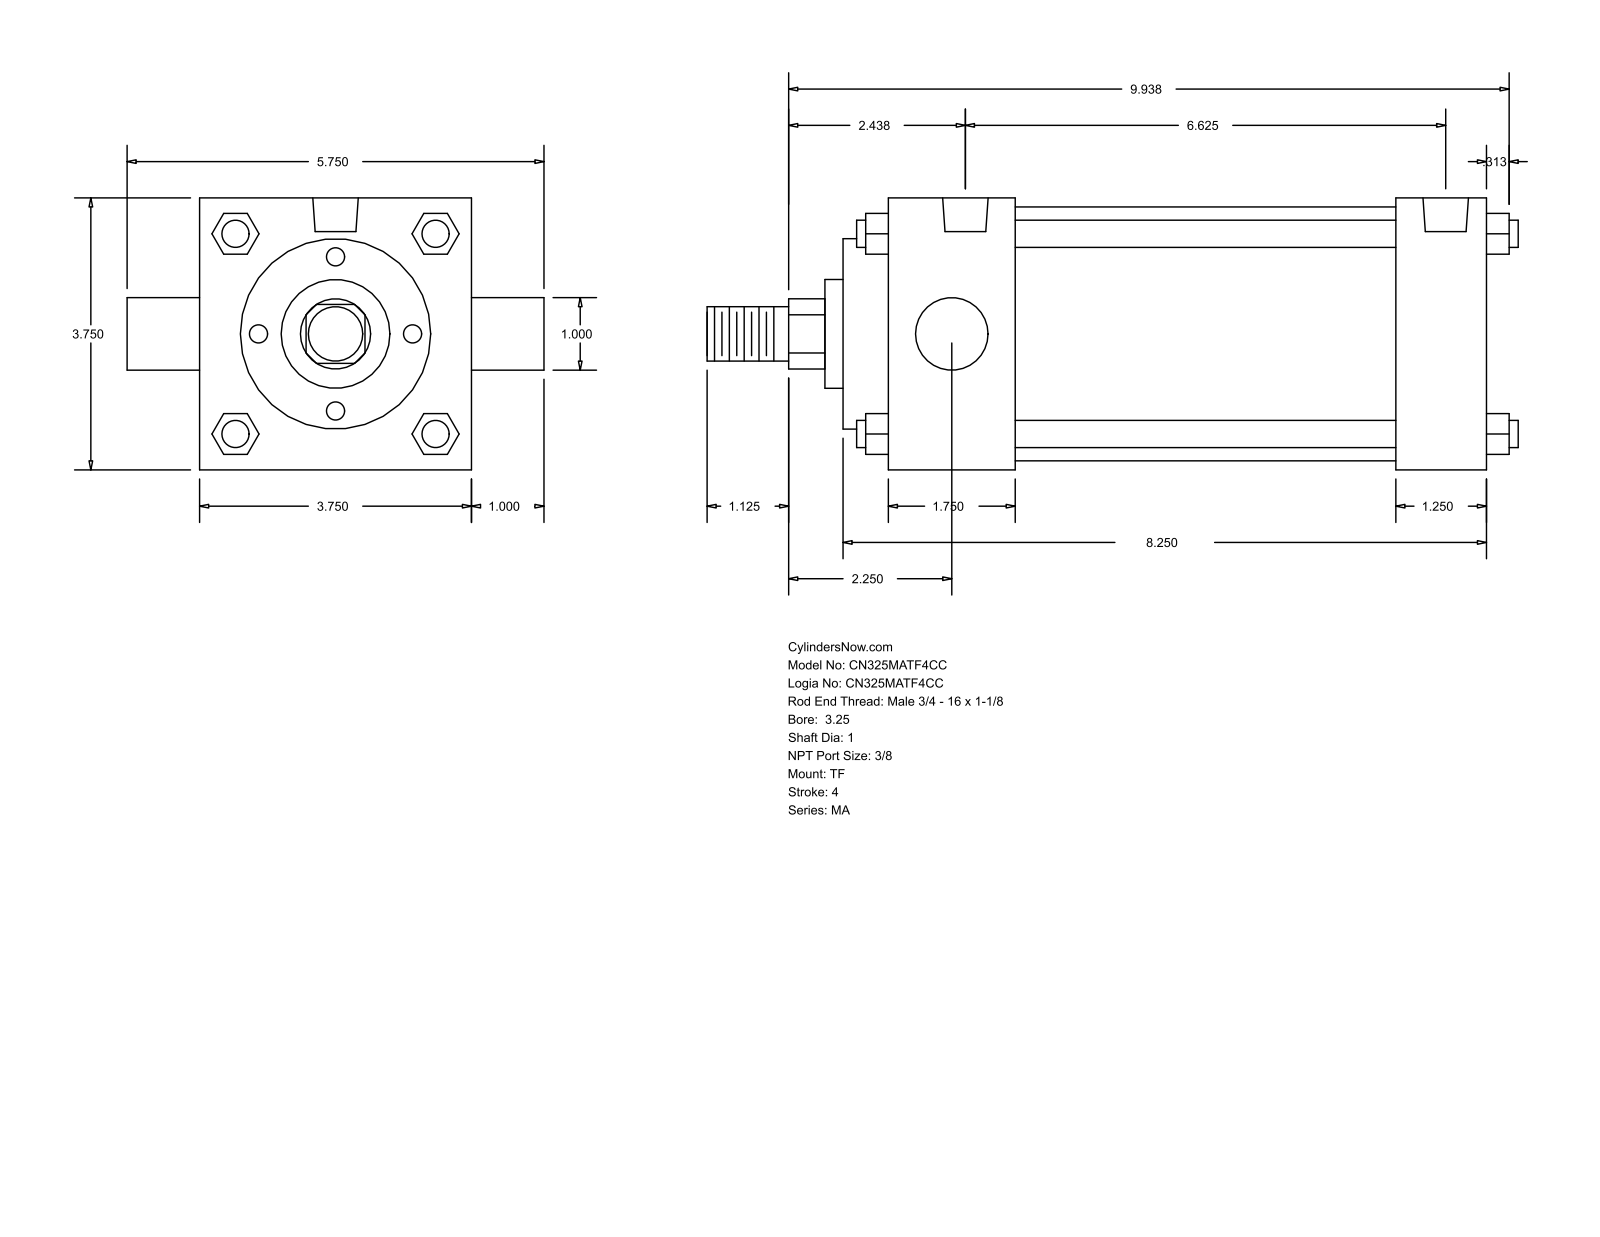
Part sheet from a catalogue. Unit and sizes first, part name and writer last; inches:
Units: inches
Overall size (bounding box): 11.187 × 5.75 × 3.75
Round holes (diameter × count): ⌀0.437 ×3, ⌀0.627 ×2
Round bosses / shafts (diameter × count): ⌀0.375 ×4, ⌀1 ×2, ⌀3.5 ×1, ⌀2.625 ×1, ⌀1.5 ×1, ⌀0.75 ×1
Partial cylindrical surfaces — rounded edges, fillets, slot ends (radius × count): R0.484 ×1
Main face-to-face distances: 3.75, 8.25, 8.875, 1.75, 7, 5.25, 6.5, 1.25, 0.625, 2.375
Hole centre spacings: 0.187, 6.438, 6.25, 6.625
Bodies: 0 solids, 122 faces (93 planar, 29 cylindrical, 0 other)
Part name (STEP PRODUCT): MA_TF__0325_1
STEP written by: GSSL Pune (CONFIG_CONTROL_DESIGN)
